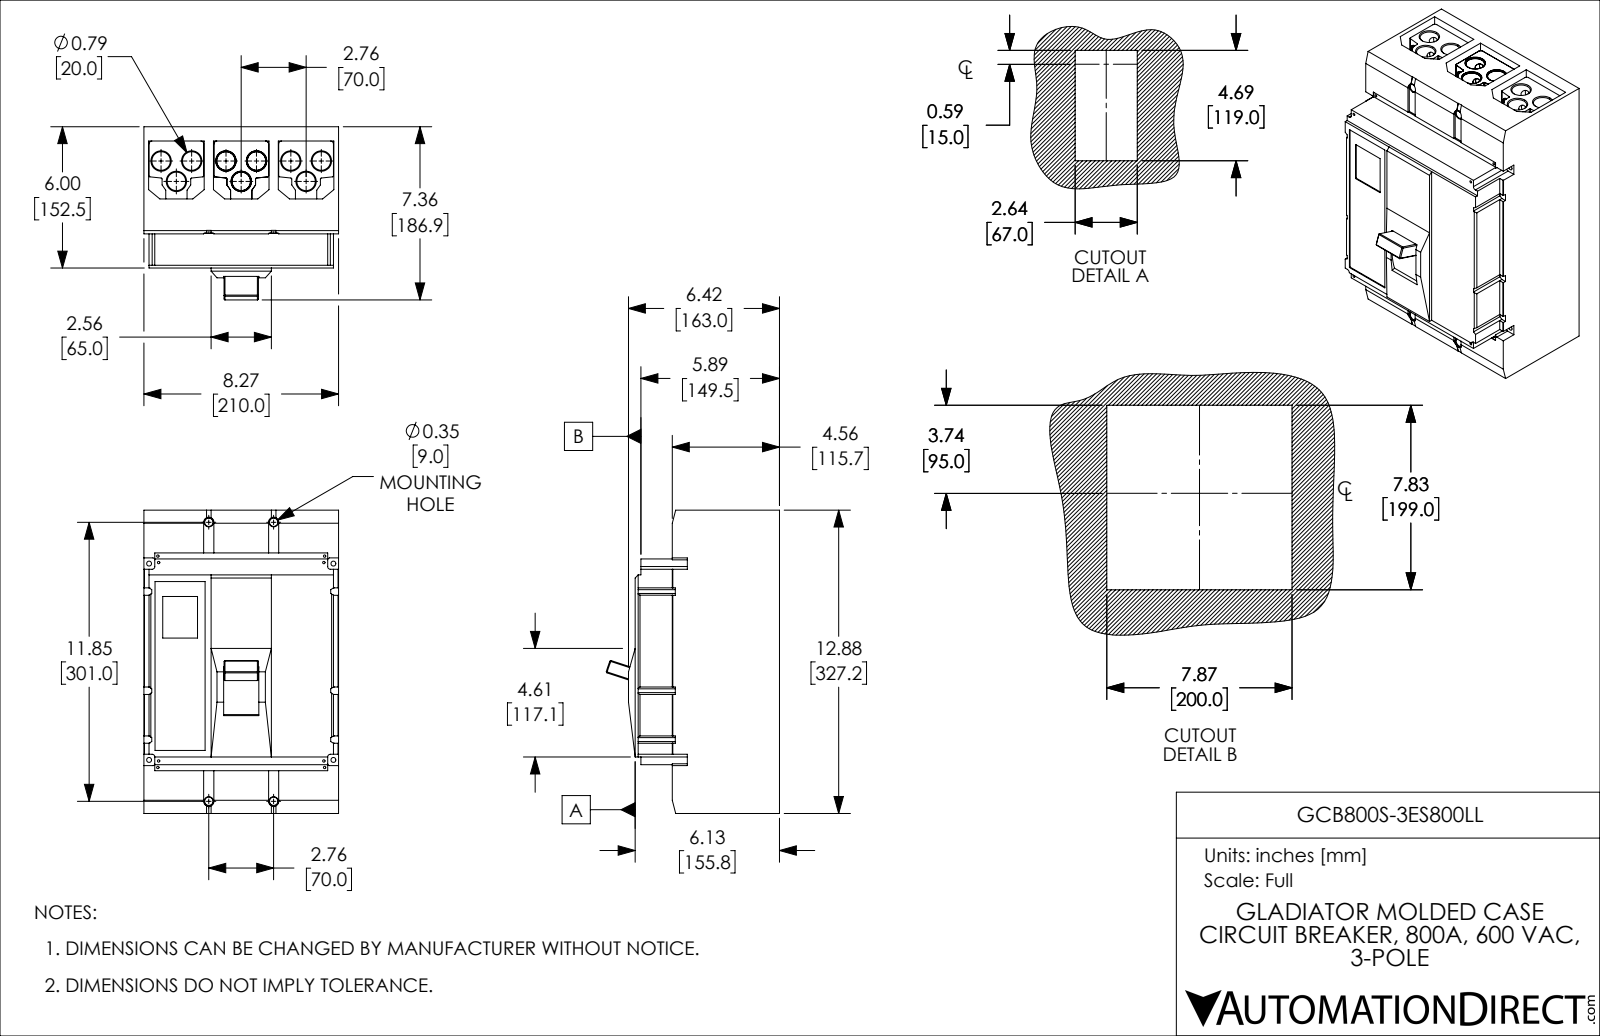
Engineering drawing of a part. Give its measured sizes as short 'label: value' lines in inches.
name: GCB800S-3ES800LL
written by: SolidWorks 2021 (CONFIG_CONTROL_DESIGN)
unit: in
bodies: 9 solids, 1758 faces (450 planar, 778 cylindrical, 530 other)
size: 12.882 × 8.268 × 7.358
volume: 540.2 in³; area: 832.4 in²
holes: 18× ⌀0.472, 12× ⌀0.268, 10× ⌀0.566, 9× ⌀0.787, 8× ⌀0.102, 8× ⌀0.566, 4× ⌀0.209, 4× ⌀0.354
rounds: 18× R0.039, 12× R0.354, 6× R0.118, 4× R0.079, 4× R0.114, 4× R0.217, 1× R3.227, 1× R3.885
face distances: 8.268, 0.61, 2.756, 1.969, 10.913, 0.02, 6.004, 5.394, 2.362, 2.343
hole spacings: 11.512, 11.181, 2.741, 2.741, 2.756, 12.452, 0.533, 5.481
